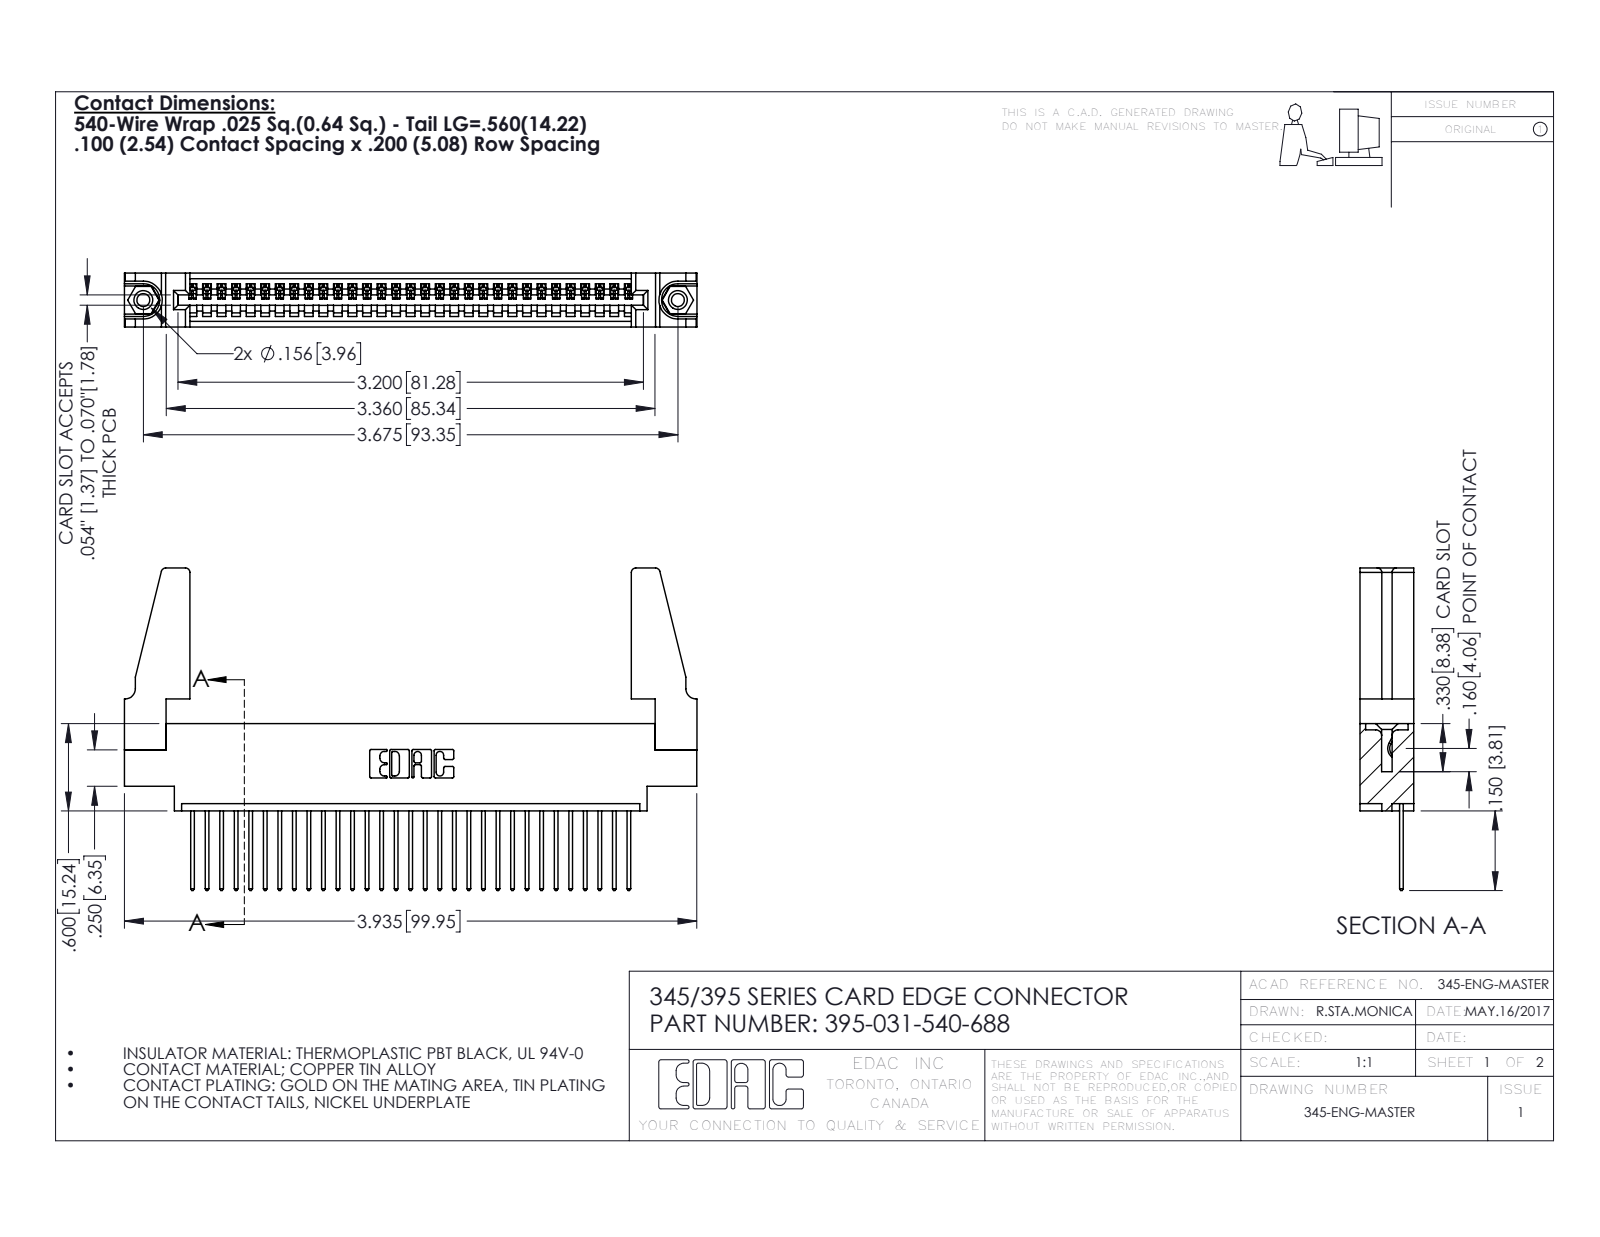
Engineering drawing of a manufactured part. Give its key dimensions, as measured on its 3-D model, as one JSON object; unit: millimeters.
{"part_name": "345-220-078_345-220-088; 395-031-540-688; 345 Part_0.170 Offset - 0.156 Dia-TH; 345-250-001_345-250-001-102 (+1 more)", "step_written_by": "SolidWorks 2016 (CONFIG_CONTROL_DESIGN)", "units": "millimeters", "bodies": {"solids": 36, "faces": 2052, "planar": 1396, "cylindrical": 640, "other": 16}, "overall_size": [100, 56.3, 9.4], "volume_mm3": 12600, "surface_area_mm2": 15810, "round_holes": [[2.3, 2], [3.2, 2], [4, 2], [1.6, 1]], "round_bosses_or_shafts": [[3.9, 2]], "partial_cylinders_radius": [[0.2, 62], [0.3, 62], [0.3, 22], [0.8, 8], [0.2, 6], [0.8, 6], [0.7, 3], [0.8, 2]], "face_to_face_distances": [1.8, 9.4, 7.6, 2.5, 6.9, 0.6, 5.1, 5.7, 4.4, 3.8], "hole_center_spacings": [6.9, 87.4, 93.3]}
